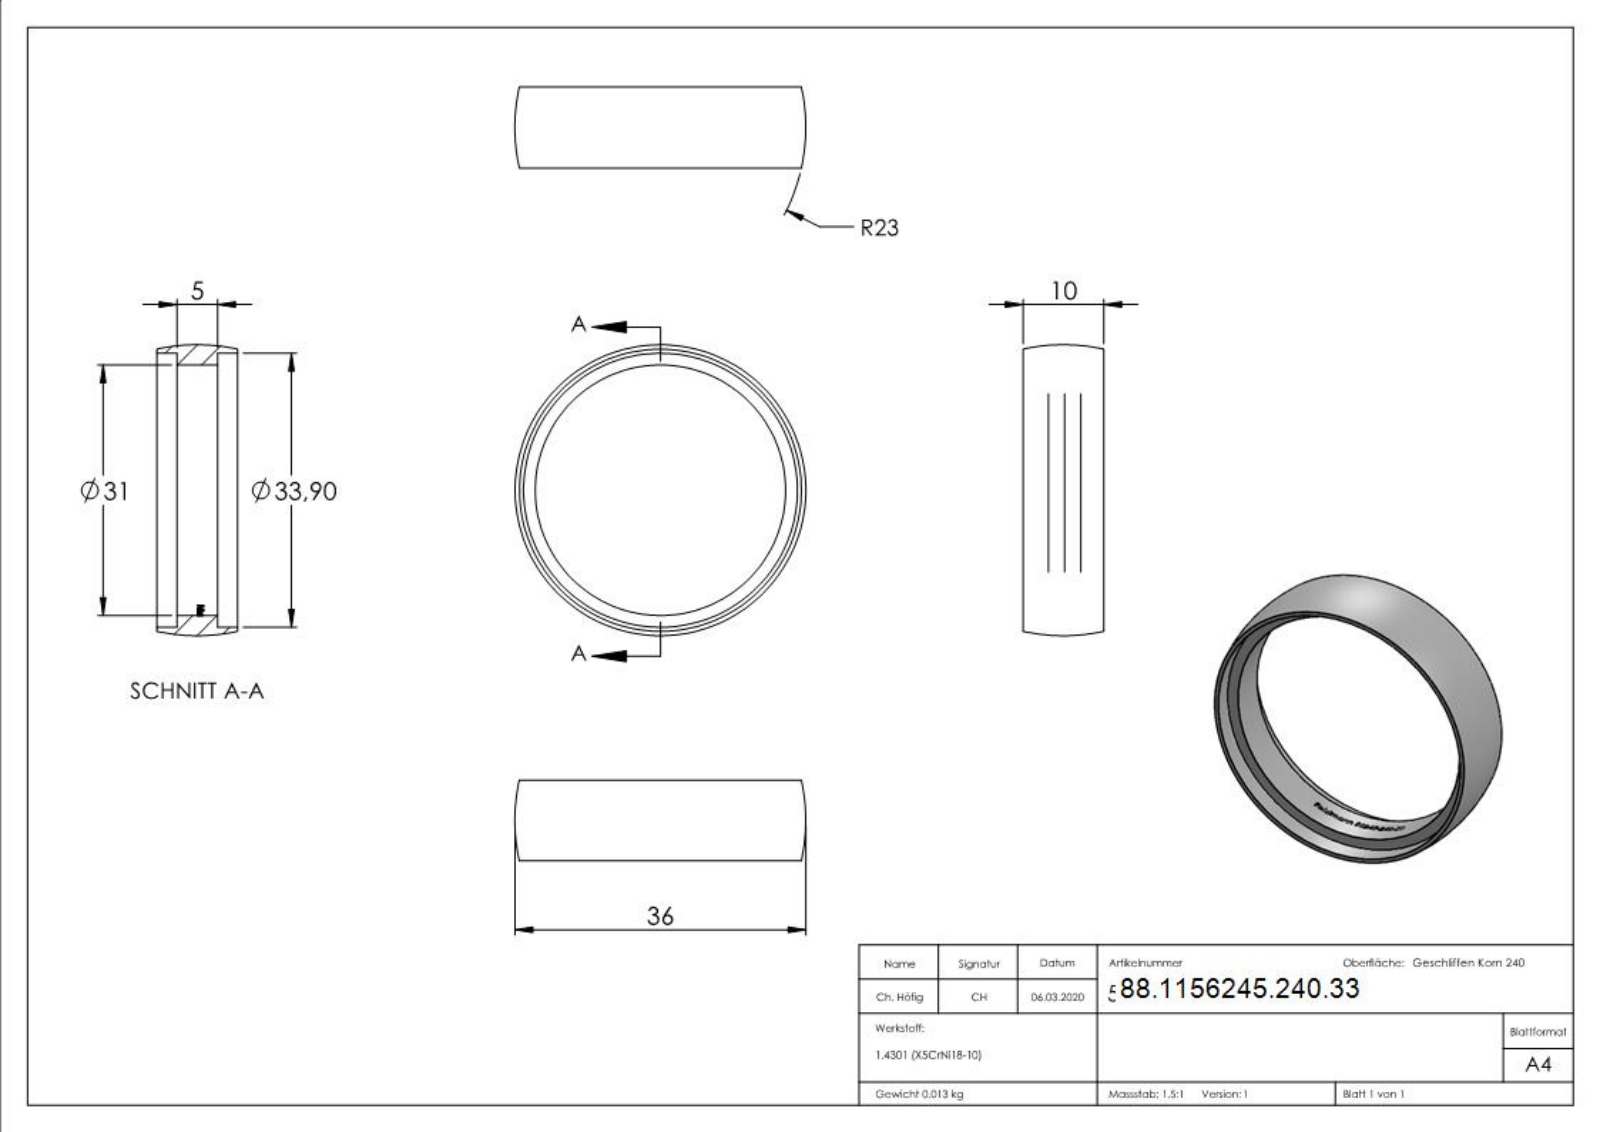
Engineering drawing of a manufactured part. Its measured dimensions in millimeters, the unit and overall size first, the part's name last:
Units: millimetres
Overall size (bounding box): 36 × 36 × 10
Round holes (diameter × count): ⌀31 ×1, ⌀33.9 ×1
Partial cylindrical surfaces — rounded edges, fillets, slot ends (radius × count): R15.6 ×1
Main face-to-face distances: 5, 2.5, 7.5, 10, 2.2, 1.78, 7.78, 0.53, 4.65, 5.26
Volume: 1 687 mm³ · Surface area: 2 558 mm²
Bodies: 1 solid, 278 faces (125 planar, 30 cylindrical, 123 other)
Part name (STEP PRODUCT): 56245-240-33
STEP written by: SolidWorks 2015 (CONFIG_CONTROL_DESIGN)
